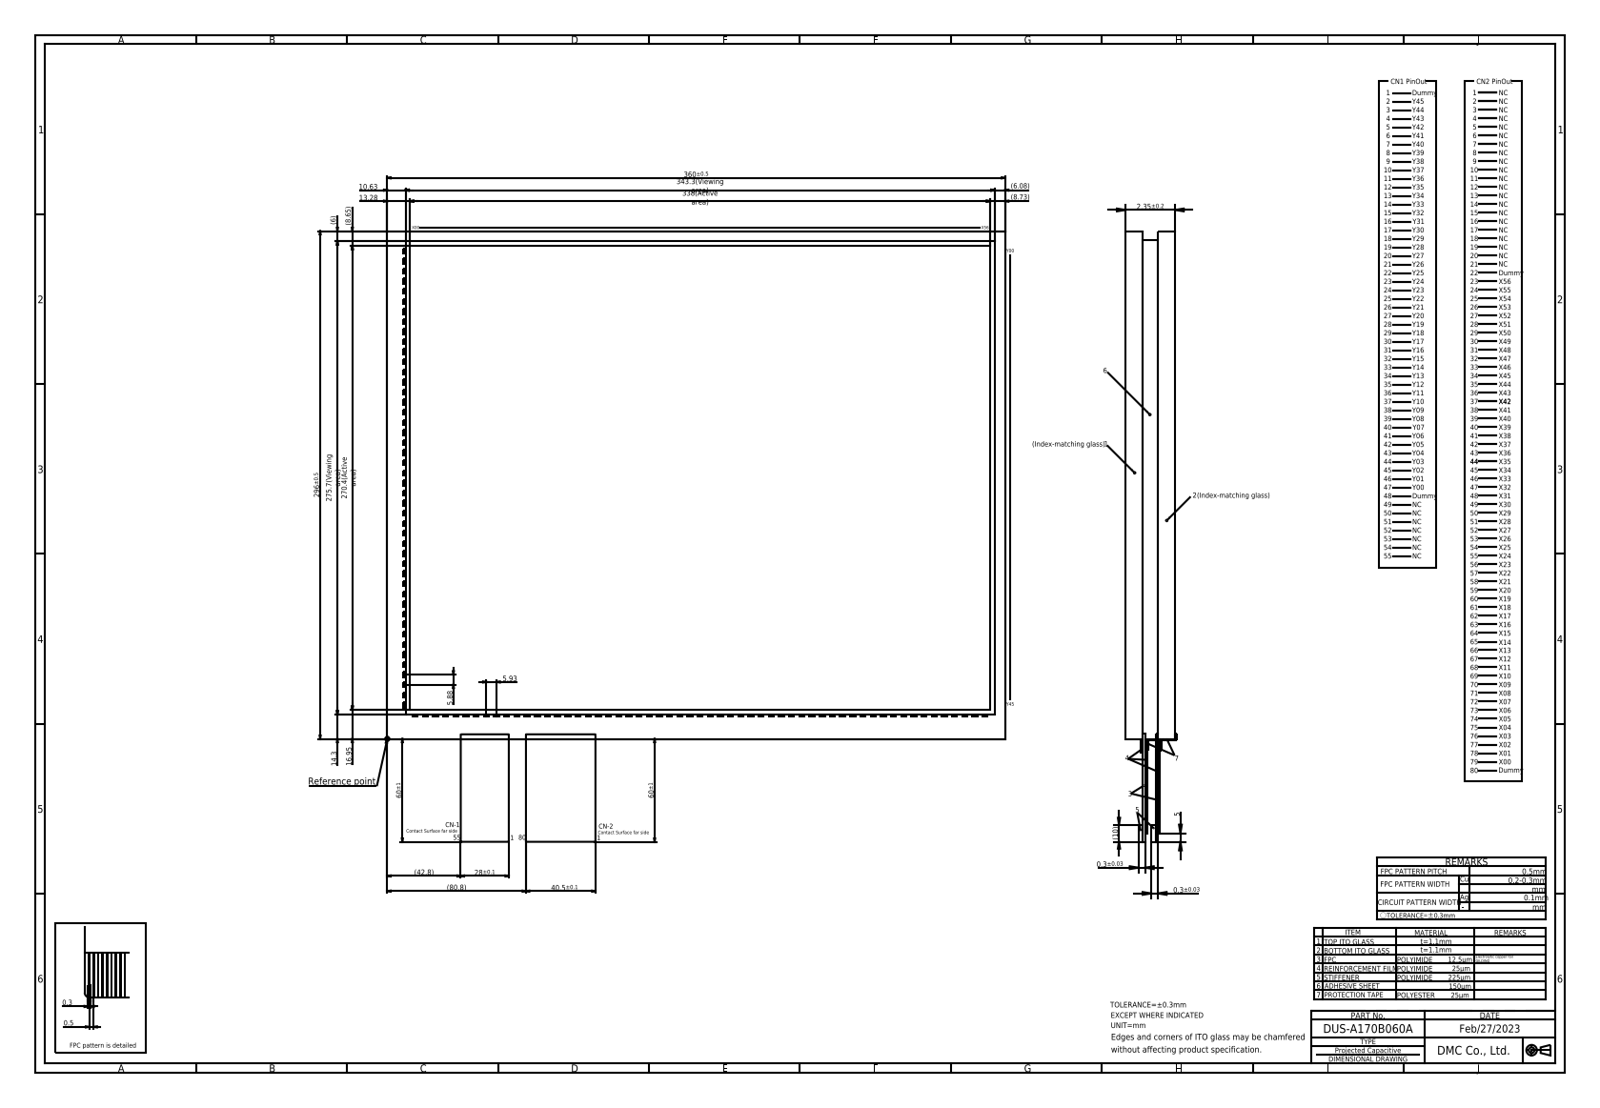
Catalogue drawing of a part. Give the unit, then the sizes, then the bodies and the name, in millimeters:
Units: millimetres
Overall size (bounding box): 504 × 415.2 × 2.35
Partial cylindrical surfaces — rounded edges, fillets, slot ends (radius × count): R0.2 ×4
Main face-to-face distances: 2.35, 1.1, 1.2, 1.15, 1.25, 1, 2.25, 296, 360, 0.8
Volume: 250 672 mm³ · Surface area: 224 757 mm²
Bodies: 1 solid, 578 faces (574 planar, 4 cylindrical, 0 other)
Part name (STEP PRODUCT): DUS-A170B060A
STEP written by: Autodesk Inventor 2020 (CONFIG_CONTROL_DESIGN)
